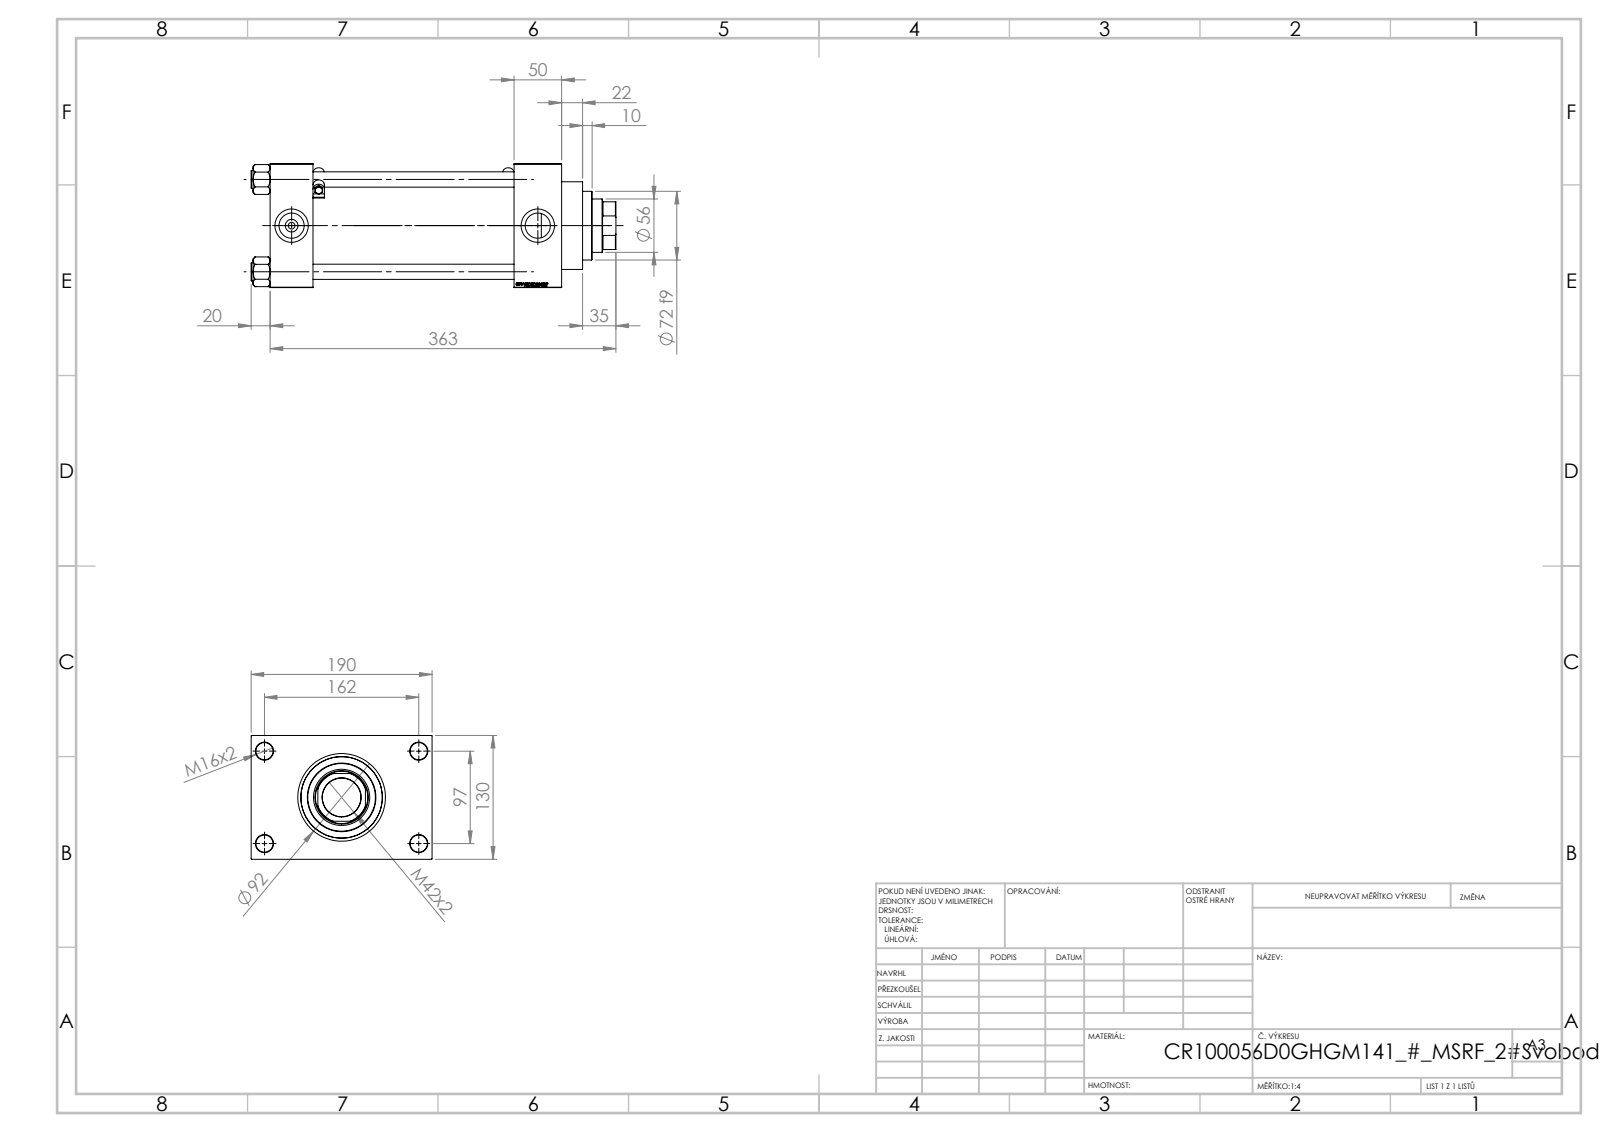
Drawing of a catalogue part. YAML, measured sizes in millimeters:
part_name: "V215CR_D_TYCINKA; V215_VC_A; V215CR_VCP_D; MSRF_MSRG1 (+2 more)"
step_written_by: "SolidWorks 2019 (CONFIG_CONTROL_DESIGN)"
units: millimeters
bodies: {solids: 13, faces: 1215, planar: 581, cylindrical: 116, other: 518}
overall_size: [383, 190, 130]
volume: 3229000
surface_area: 510455
round_holes:
  - {diameter: 16, count: 4}
  - {diameter: 18, count: 4}
  - {diameter: 7, count: 2}
  - {diameter: 26.44, count: 2}
  - {diameter: 35, count: 2}
  - {diameter: 40.5, count: 1}
  - {diameter: 56, count: 1}
  - {diameter: 59, count: 1}
  - {diameter: 76, count: 1}
  - {diameter: 85.5, count: 1}
  - {diameter: 100, count: 1}
round_bosses_or_shafts:
  - {diameter: 19, count: 4}
  - {diameter: 5, count: 2}
  - {diameter: 2.5, count: 2}
  - {diameter: 106, count: 1}
  - {diameter: 92, count: 1}
  - {diameter: 72, count: 1}
partial_cylinders:
  - {radius: 0.5, count: 12}
  - {radius: 6, count: 4}
  - {radius: 27, count: 1}
face_to_face_distances: [130, 50, 45, 256, 211, 306, 261, 160, 30, 190]
hole_center_spacings: [32.55, 68.52, 94.41, 96.9, 102.27, 129.45, 161.73, 97]
